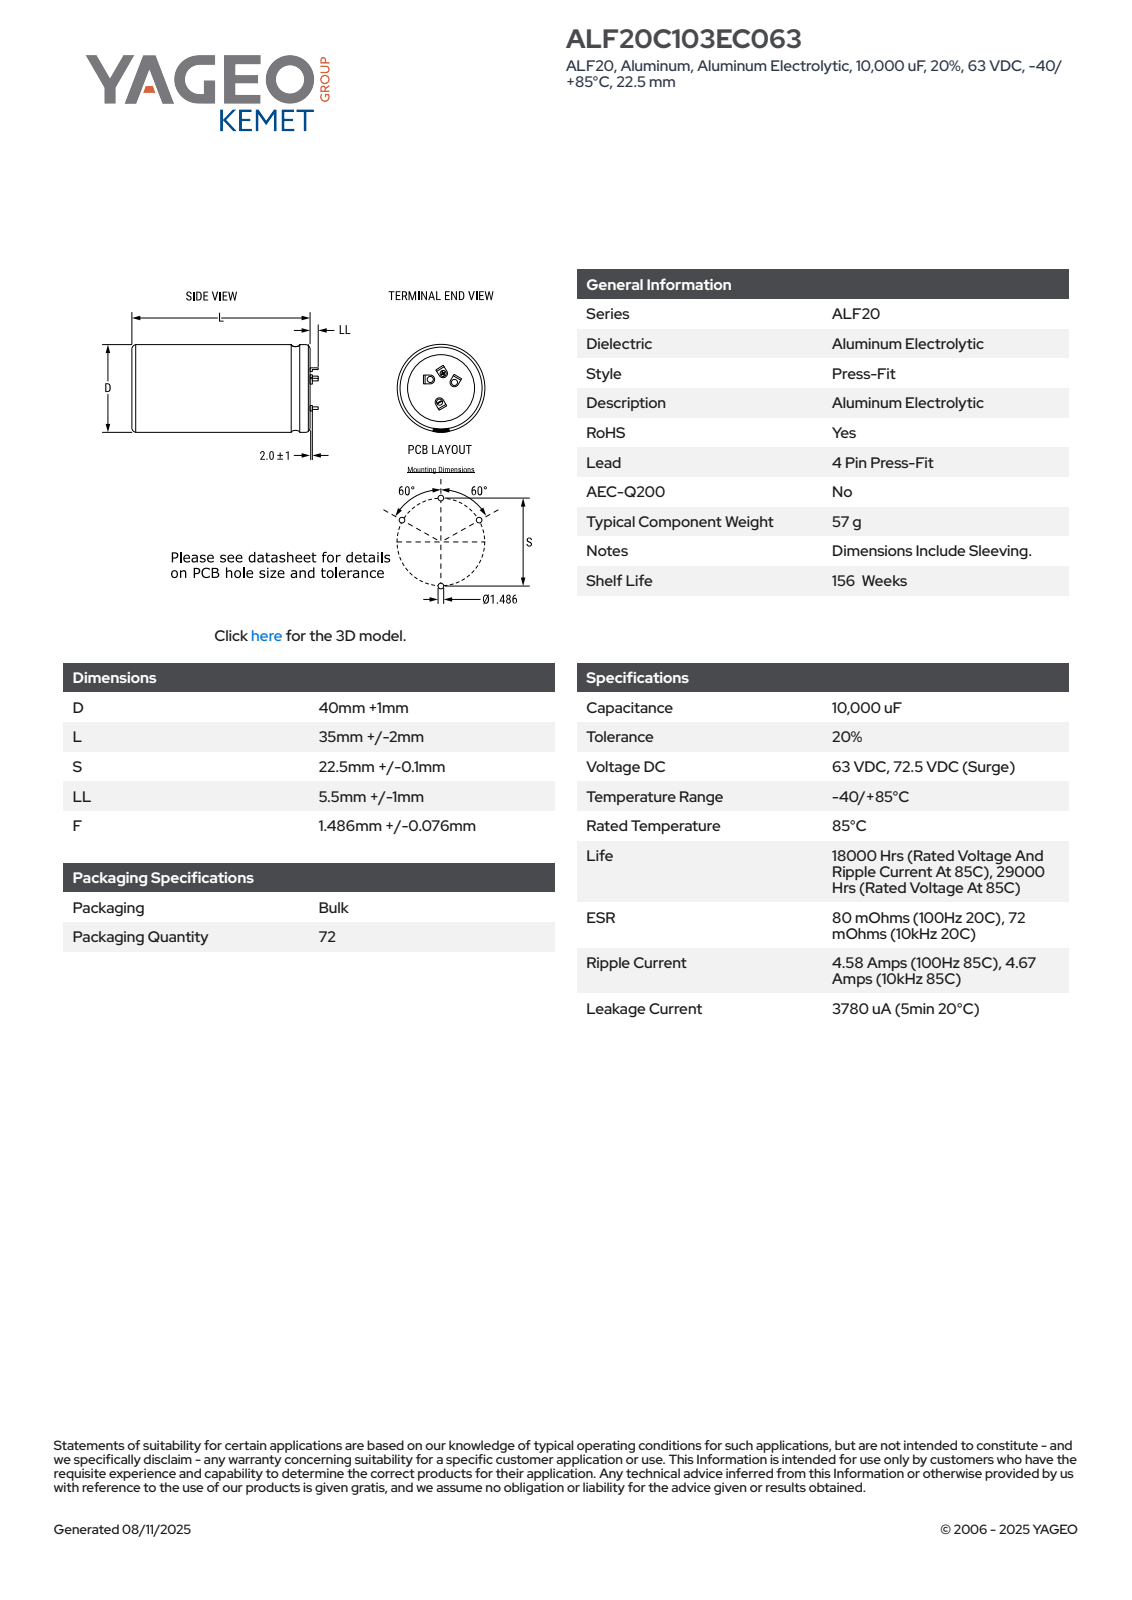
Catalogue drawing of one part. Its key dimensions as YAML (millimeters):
part_name: "CARS_ALF2040C_40X35_D41L37S22.5LL6.5"
step_written_by: "SolidWorks 2014 (AUTOMOTIVE_DESIGN)"
units: millimeters
bodies: {solids: 6, faces: 333, planar: 139, cylindrical: 138, other: 56}
overall_size: [43.62, 41, 41]
volume: 48587
surface_area: 7703
round_bosses_or_shafts:
  - {diameter: 3.5, count: 4}
  - {diameter: 41, count: 1}
partial_cylinders:
  - {radius: 0.15, count: 50}
  - {radius: 0.1, count: 8}
  - {radius: 0.42, count: 8}
  - {radius: 2.5, count: 3}
  - {radius: 2.52, count: 1}
face_to_face_distances: [37, 37.01, 0.8, 5, 3, 3.01, 40.01, 5.01, 6.61, 3.6]
